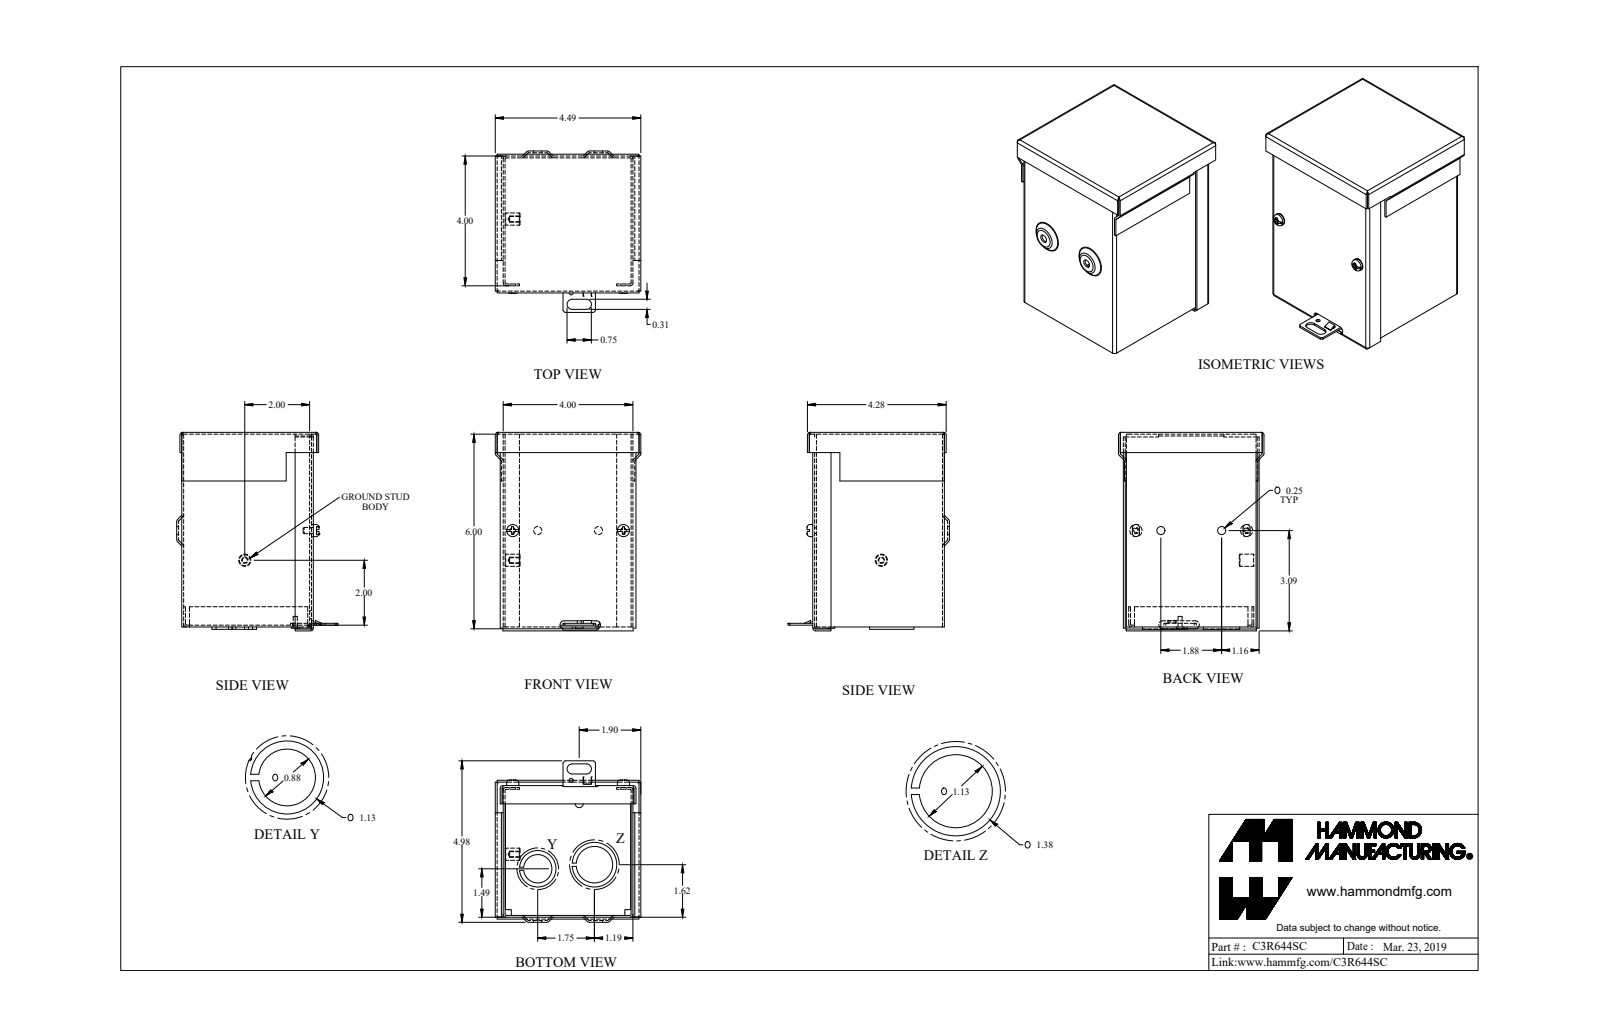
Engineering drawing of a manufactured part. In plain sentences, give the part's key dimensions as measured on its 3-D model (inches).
The part is named "C3R644SC_Default". Its 3-D file was written by "SolidWorks 2019 (CONFIG_CONTROL_DESIGN)". It is 9 solids with 316 faces: 175 planar, 91 cylindrical and 50 other. Overall it measures 6.12 by 4.977 by 4.489 inches. Its volume is 9.623 cubic inches and its surface area 342.8 square inches. Round holes: 2 of diameter 0.17, 2 of diameter 0.25, 1 of diameter 0.125, 1 of diameter 0.137, 1 of diameter 0.156, 1 of diameter 0.875, 1 of diameter 1.125. Round bosses or shafts: 3 of diameter 0.375, 2 of diameter 0.19, 1 of diameter 1.375, 1 of diameter 1.125, 1 of diameter 0.125. Partial cylindrical surfaces (rounded edges, fillets, slot ends): 21 of radius 0.029, 21 of radius 0.086, 8 of radius 0.125, 4 of radius 0.109, 2 of radius 0.156. The main face-to-face distances are 0.057, 4, 3.943, 3.886, 4.057, 0.057, 5.886, 0.114, 5.943, 5.943. The hole center spacings are 0.77, 2.644, 0.763, 1.754, 1.875, 1.938, 2.38, 2.699.
